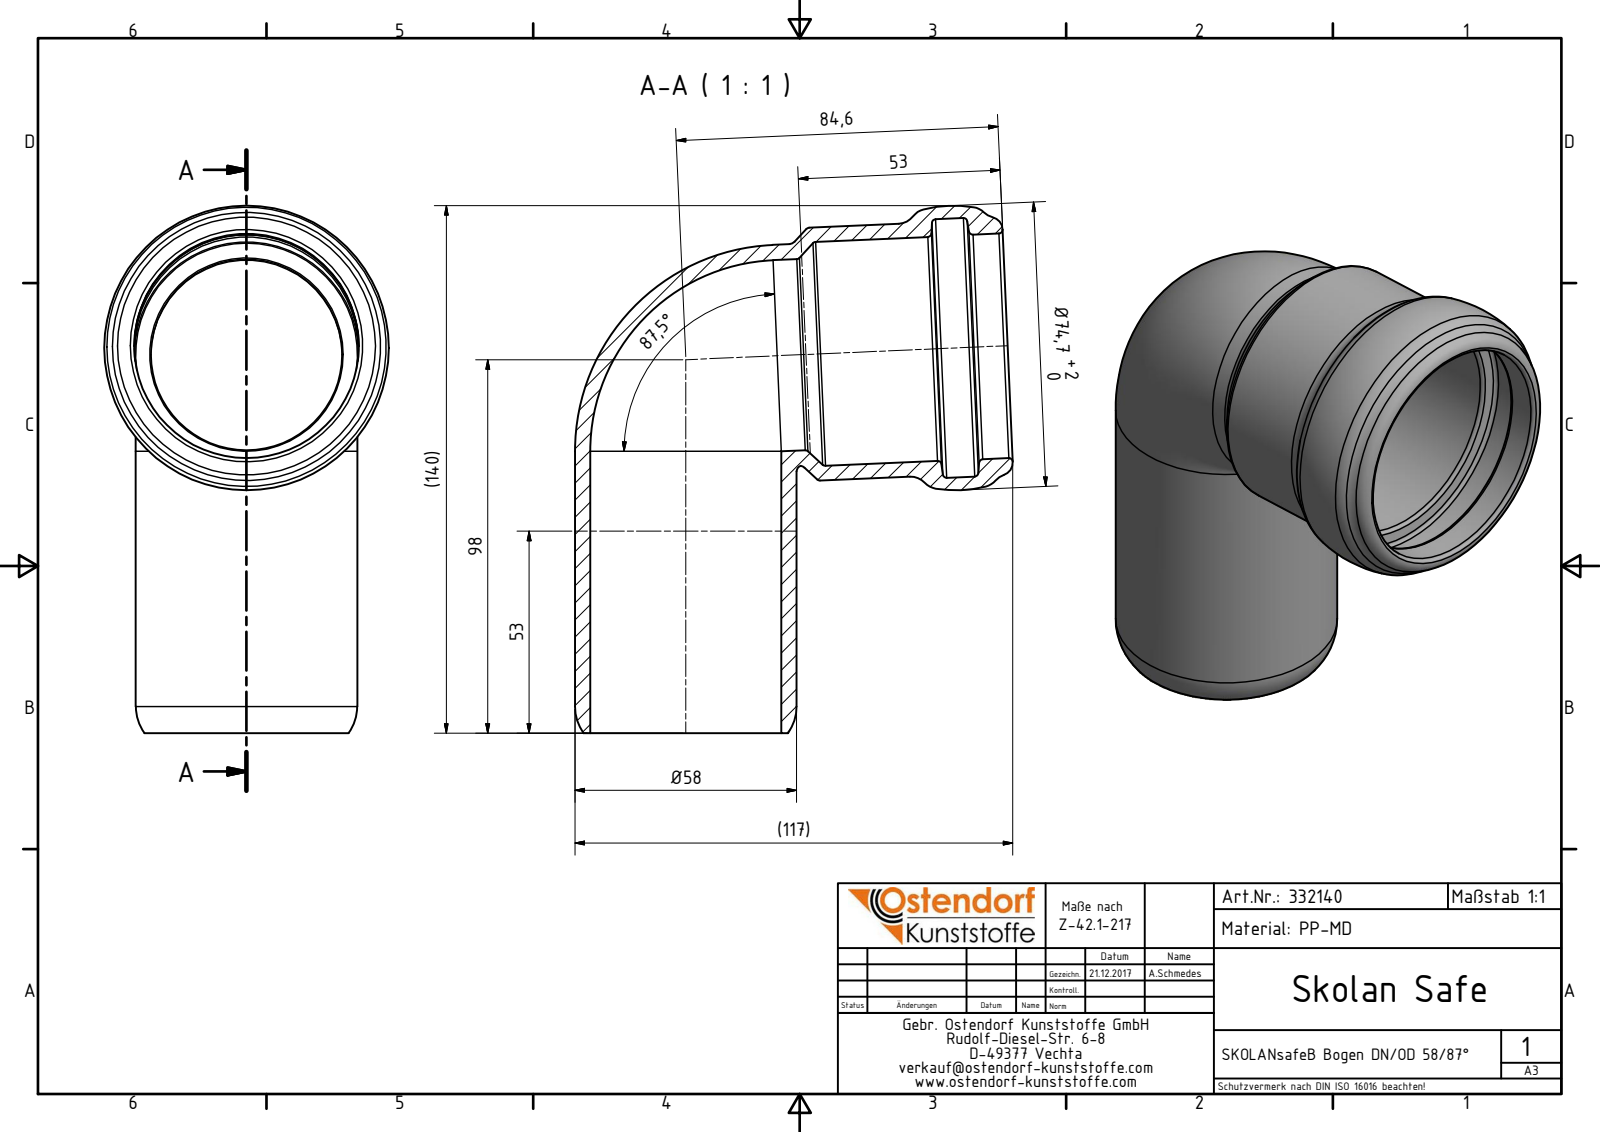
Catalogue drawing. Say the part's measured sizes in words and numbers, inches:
The part is named "332140 SKOLANsafeB Bogen DN_OD 58_87°". Its 3-D file was written by "Autodesk Inventor 2016 (AUTOMOTIVE_DESIGN)". It is 1 solid with 32 faces: 1 planar, 8 cylindrical and 23 other. Overall it measures 5.45 by 4.526 by 2.941 inches. Its volume is 7.72 cubic inches and its surface area 101.6 square inches. Round holes: 2 of diameter 1.976, 1 of diameter 2.315, 1 of diameter 2.323, 1 of diameter 2.673. Round bosses or shafts: 2 of diameter 2.291, 1 of diameter 2.614.
